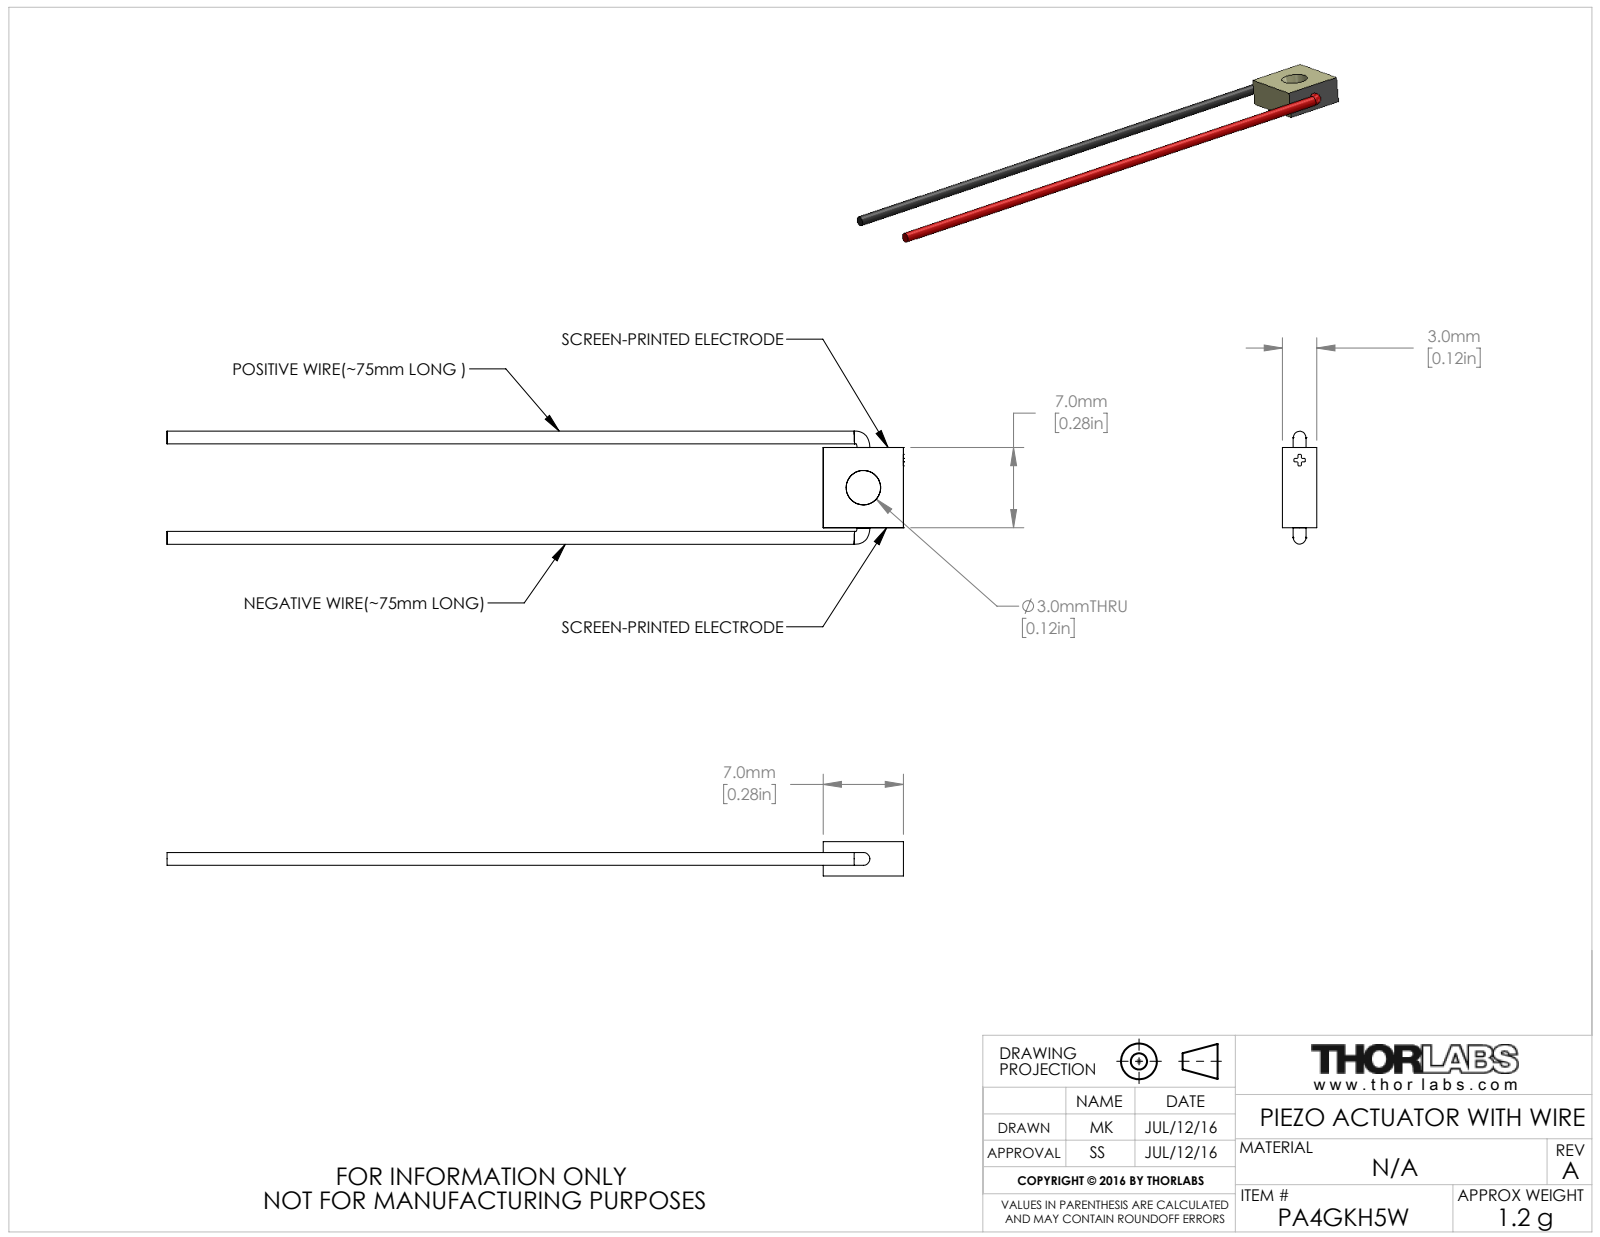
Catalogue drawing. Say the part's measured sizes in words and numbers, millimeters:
The part is named "CTN009267". Its 3-D file was written by "SolidWorks 2016 (AUTOMOTIVE_DESIGN)". It is 3 solids with 21 faces: 11 planar, 2 cylindrical and 8 other. Overall it measures 64.29 by 9.88 by 3 millimeters. Its volume is 247 cubic millimeters and its surface area 632 square millimeters. Round holes: 1 of diameter 3. The main face-to-face distances are 7, 3, 64.29, 57.29.
